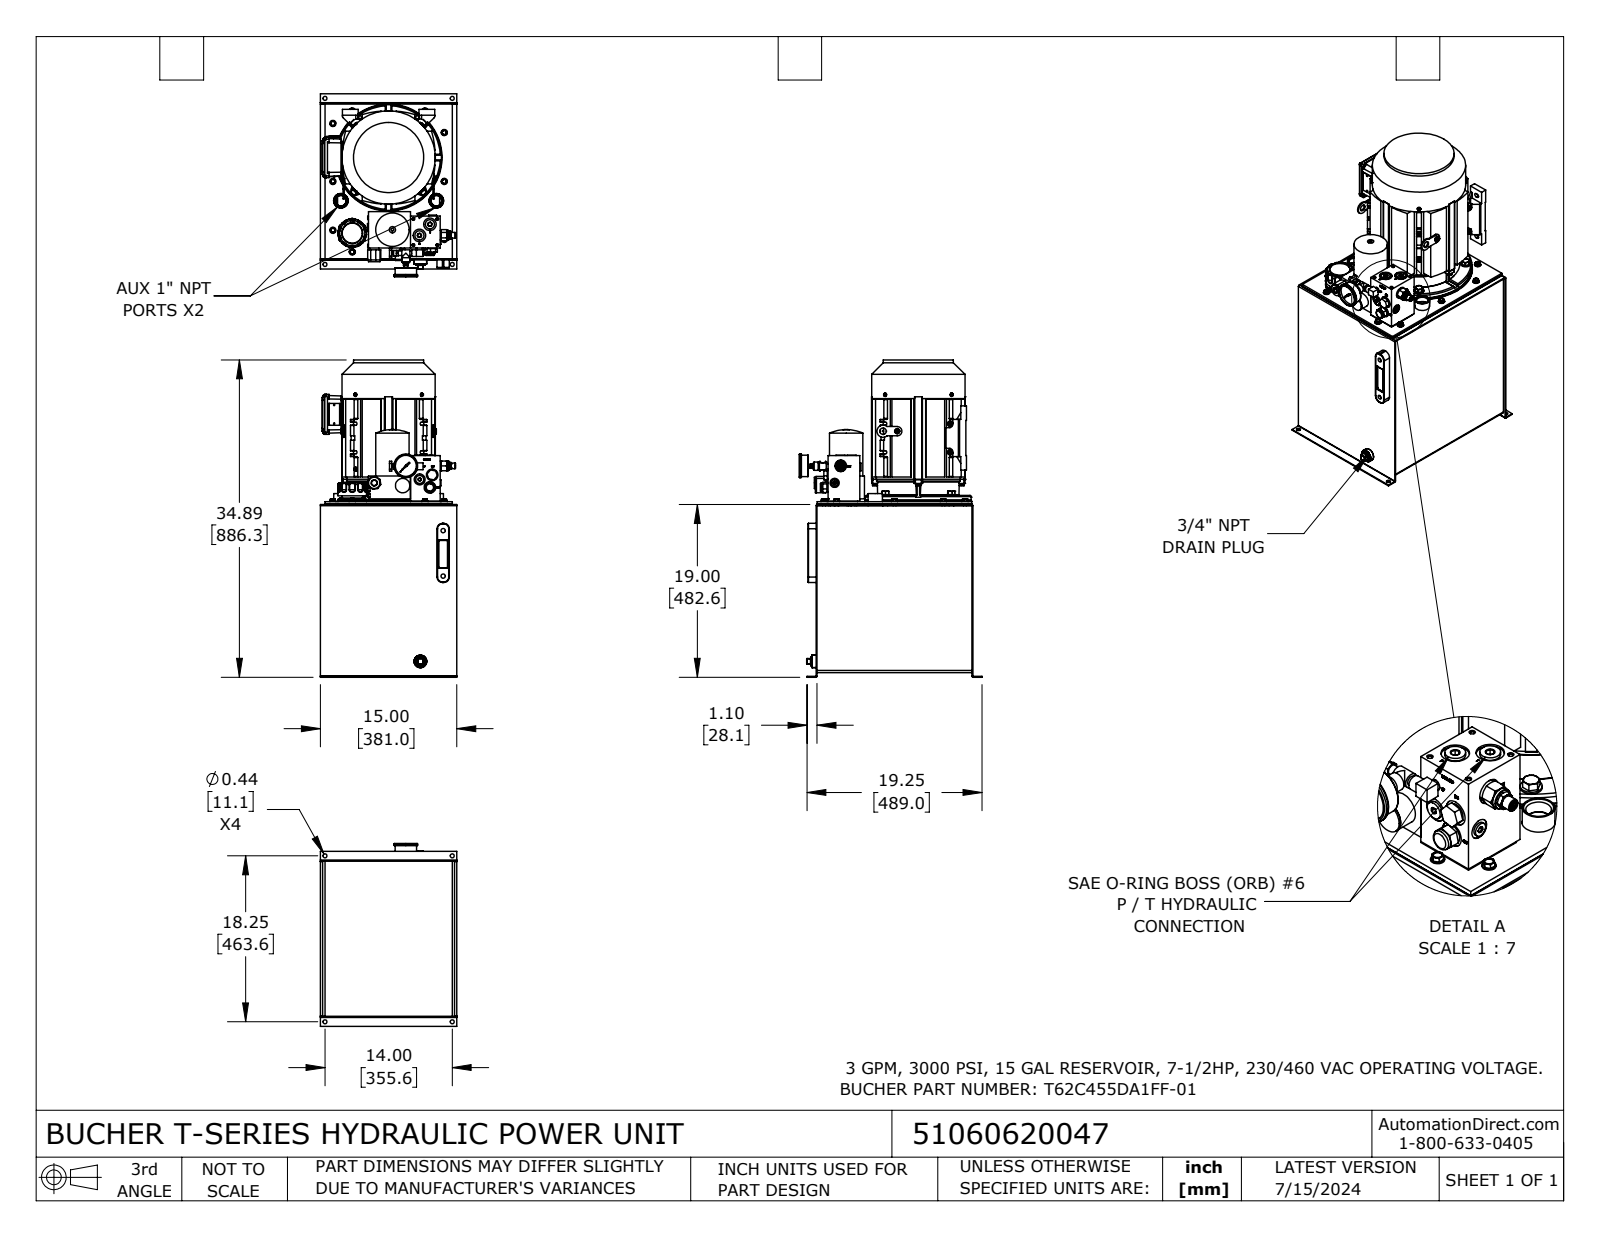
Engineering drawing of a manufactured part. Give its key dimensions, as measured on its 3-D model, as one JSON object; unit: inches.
{"part_name": "51060620047", "step_written_by": "SolidWorks 2023 (CONFIG_CONTROL_DESIGN)", "units": "inches", "bodies": {"solids": 119, "faces": 5112, "planar": 2513, "cylindrical": 1694, "other": 905}, "overall_size": [34.894, 20.112, 15], "volume_in3": 1643, "surface_area_in2": 5678, "round_holes": [[0.437, 19], [0.236, 11], [0.5, 11], [0.197, 10], [0.563, 10], [0.315, 9], [0.201, 8], [0.268, 8], [0.12, 6], [0.19, 6], [0.531, 6], [0.807, 5]], "round_bosses_or_shafts": [[0.676, 10], [0.313, 10], [0.551, 9], [0.472, 9], [0.373, 6], [0.5, 5], [0.25, 5], [1.062, 4]], "partial_cylinders_radius": [[0.02, 188], [0.079, 68], [0.039, 52], [0.25, 36], [0.063, 20], [0.118, 20], [0.375, 16], [0.05, 13]], "face_to_face_distances": [0.104, 0.105, 14.395, 17.145, 14.5, 14.291, 17.25, 0.25, 17.041, 18.385], "hole_center_spacings": [3.15, 3.469, 1.441, 1.442, 2.497, 6.232, 8.297, 0.78]}
